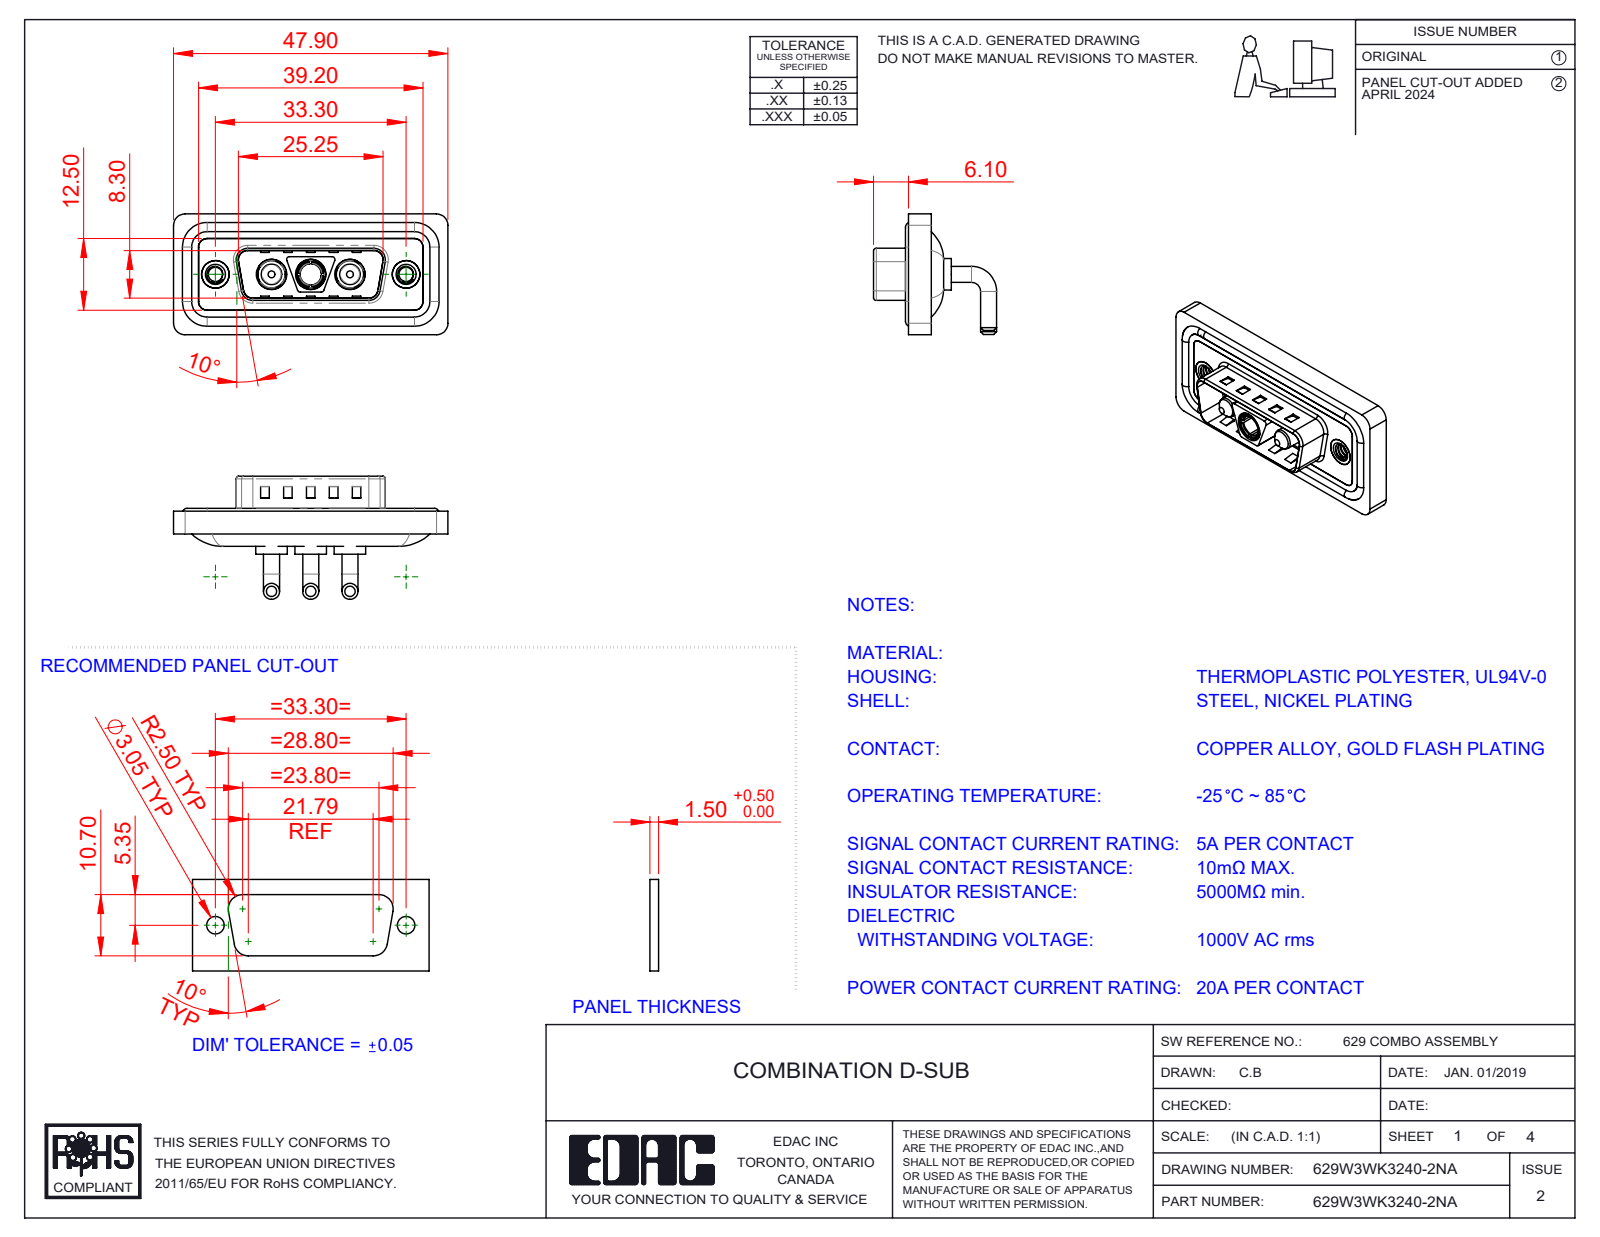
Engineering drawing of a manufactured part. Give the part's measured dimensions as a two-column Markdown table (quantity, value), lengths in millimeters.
| quantity | value |
| --- | --- |
| part name | 629W3WK3240-2NA; 629Combo Waterproof Housing_15 Contacts; 629Combo Threaded Rivet_A; Power Socket_20A RA (+4 more) |
| STEP written by | SolidWorks 2023 (CONFIG_CONTROL_DESIGN) |
| units | millimeters |
| bodies | 13 solids, 615 faces (231 planar, 254 cylindrical, 130 other) |
| overall size | 47.9 × 21.5 × 21.1 |
| volume | 5 888 mm³ |
| surface area | 9 419 mm² |
| round holes (diameter × count) | 4.85 × 3, 5.3 × 3, 2.5 × 2, 4 × 2, 4.8 × 2, 5 × 2, 3.7 × 1 |
| round bosses / shafts (diameter × count) | 2.8 × 6, 1.6 × 4, 5.5 × 3, 5.2 × 3, 4.75 × 3, 3.75 × 3, 4.9 × 2, 3.6 × 2 |
| partial cylindrical surfaces (radius × count) | 2 × 20, 1.5 × 18, 0.5 × 12, 1.6 × 8, 0.25 × 4, 0.6 × 4, 0.65 × 4, 0.9 × 4 |
| main face-to-face distances | 0.4, 2.9, 0.8, 1.1, 2.1, 1.6, 4.5, 3.1, 2.5, 3.7 |
| hole center spacings | 6.85, 9.8, 16.65, 23.5, 13.7, 33.3 |
